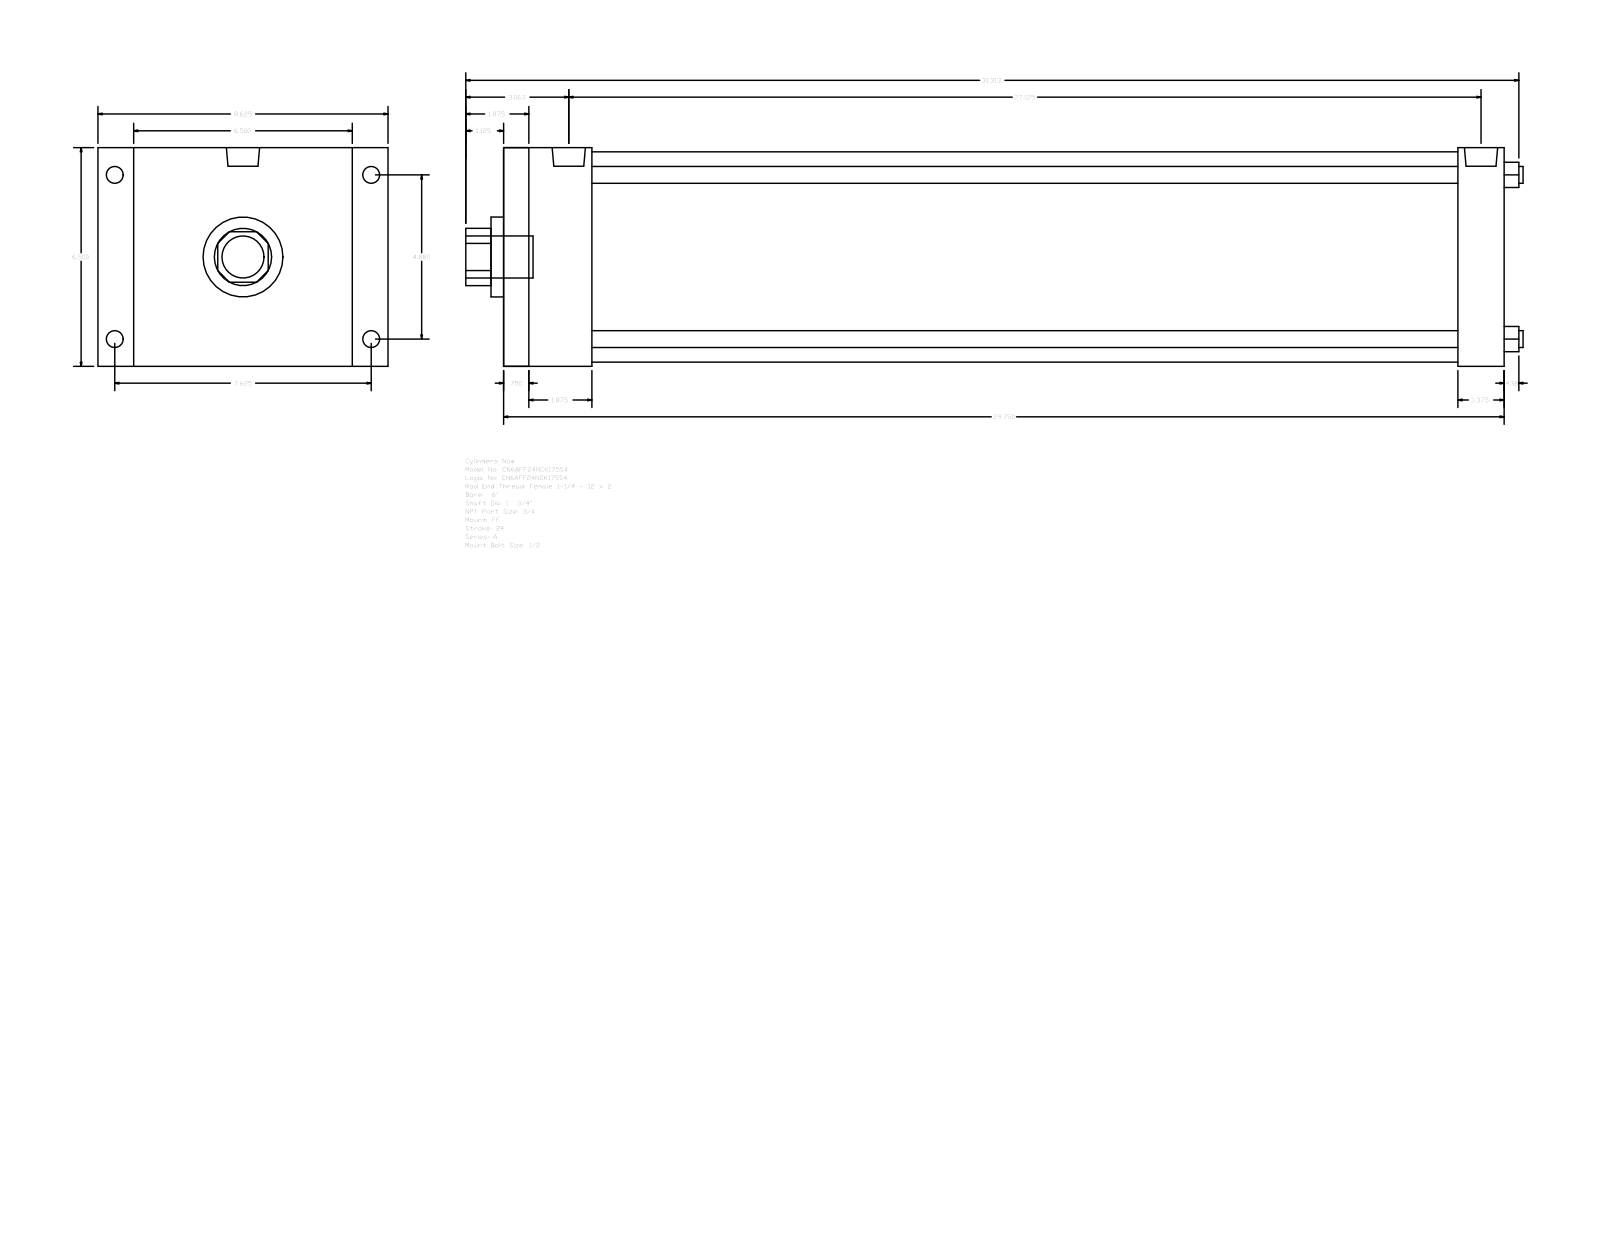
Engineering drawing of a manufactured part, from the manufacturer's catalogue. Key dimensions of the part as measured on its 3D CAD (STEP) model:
Part name (STEP PRODUCT): A_FF__0600_1.75
STEP written by: GSSL Pune (CONFIG_CONTROL_DESIGN)
Units: millimetres
Bodies: 0 solids, 92 faces (64 planar, 28 cylindrical, 0 other)
Overall size (bounding box): 798.51 × 219.07 × 165.1
Round holes (diameter × count): ⌀12.7 ×4, ⌀44.45 ×1, ⌀60.33 ×1, ⌀158.75 ×1
Round bosses / shafts (diameter × count): ⌀15.08 ×4, ⌀12.7 ×4, ⌀25.12 ×2, ⌀31.75 ×1
Partial cylindrical surfaces — rounded edges, fillets, slot ends (radius × count): R21.63 ×1
Main face-to-face distances: 165.1, 755.66, 19.05, 736.61, 66.68, 47.63, 688.98, 720.73, 701.68, 654.05
Hole centre spacings: 87.65, 123.96, 175.31
